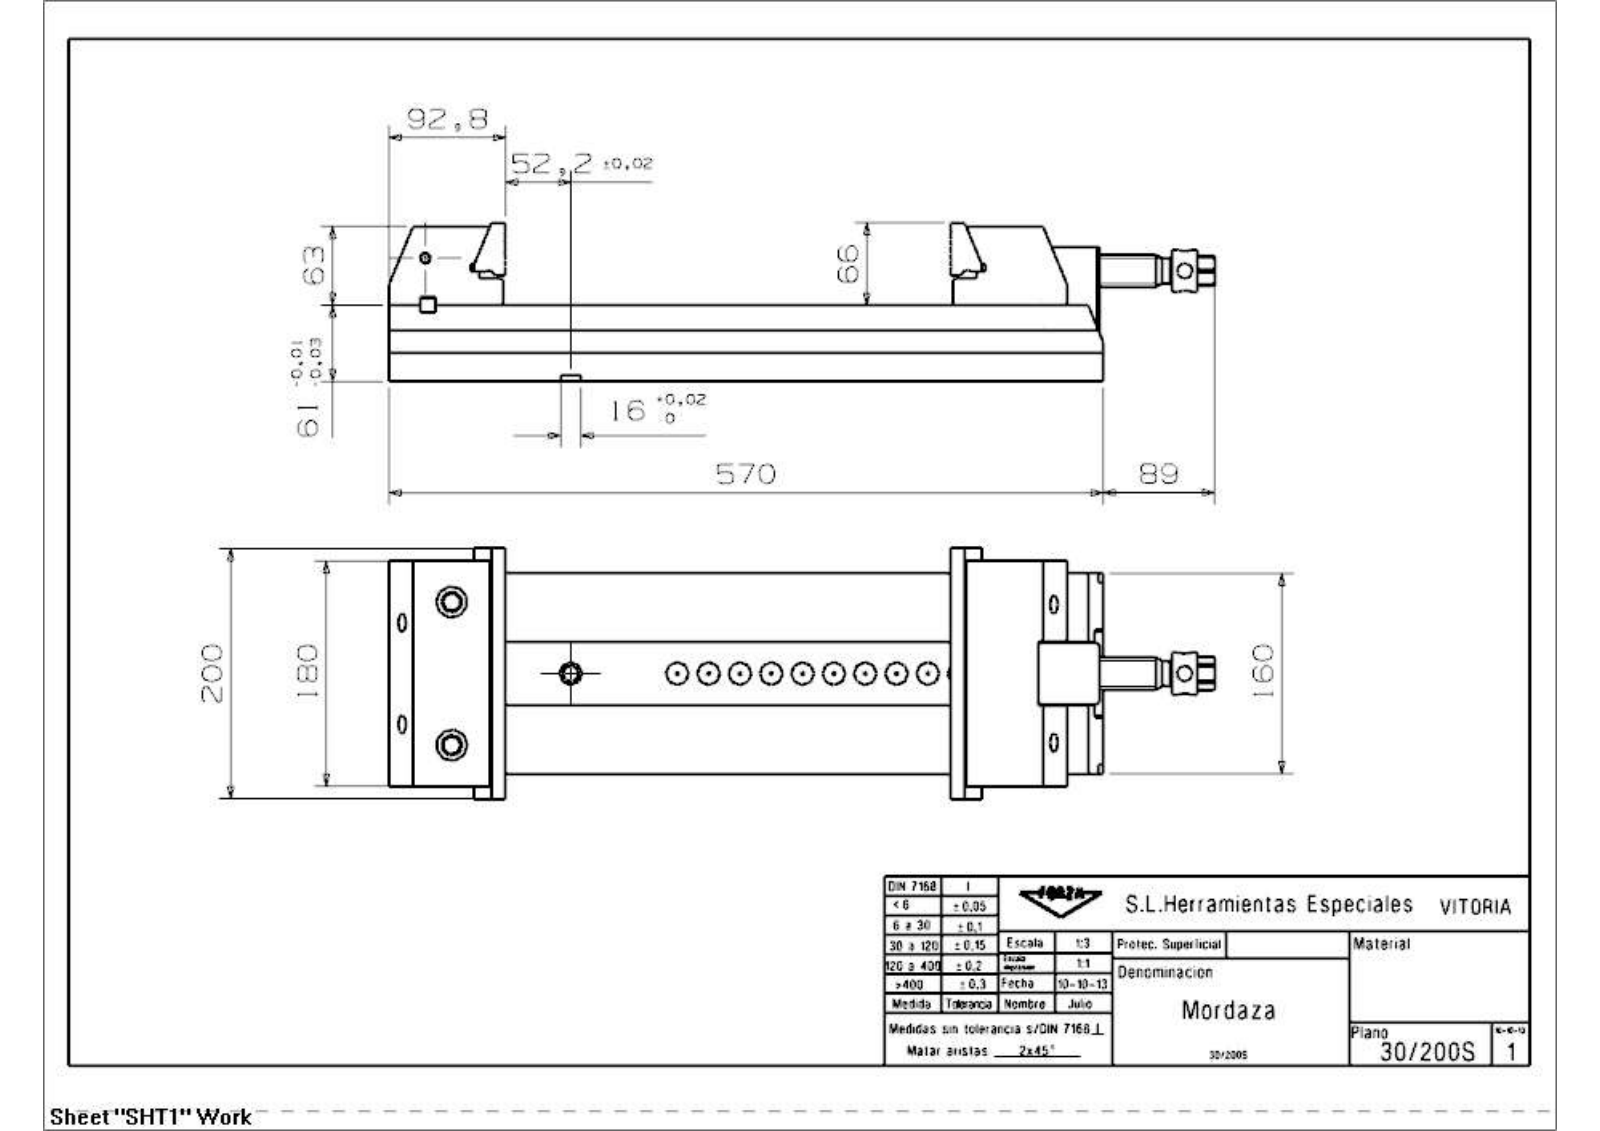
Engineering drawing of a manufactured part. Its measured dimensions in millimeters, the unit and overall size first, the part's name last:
Units: millimetres
Overall size (bounding box): 659 × 200 × 126.95
Round holes (diameter × count): ⌀15 ×6, ⌀5.19 ×5, ⌀13 ×5, ⌀6.99 ×4, ⌀8.5 ×4, ⌀10 ×4, ⌀8.78 ×3, ⌀10.58 ×3, ⌀19 ×3, ⌀12 ×2, ⌀12.38 ×2, ⌀14.38 ×2
Round bosses / shafts (diameter × count): ⌀34 ×1, ⌀33.8 ×1, ⌀26 ×1, ⌀20 ×1, ⌀16.5 ×1
Partial cylindrical surfaces — rounded edges, fillets, slot ends (radius × count): R0.4 ×24, R1.5 ×4, R8 ×4, R20 ×4, R1.6 ×2, R6 ×2, R7 ×2, R4 ×1
Main face-to-face distances: 61, 29.2, 31.8, 59.5, 7.5, 1.5, 160, 27.7, 63, 124
Hole centre spacings: 14.5, 95.5, 81, 110, 16.47, 16.55, 24.08, 30
Volume: 6 268 000 mm³ · Surface area: 651 852 mm²
Bodies: 12 solids, 484 faces (277 planar, 136 cylindrical, 71 other)
Part name (STEP PRODUCT): 30_200S_Mordaza
STEP written by: SIEMENS PLM Software NX 7.5 (CONFIG_CONTROL_DESIGN)
